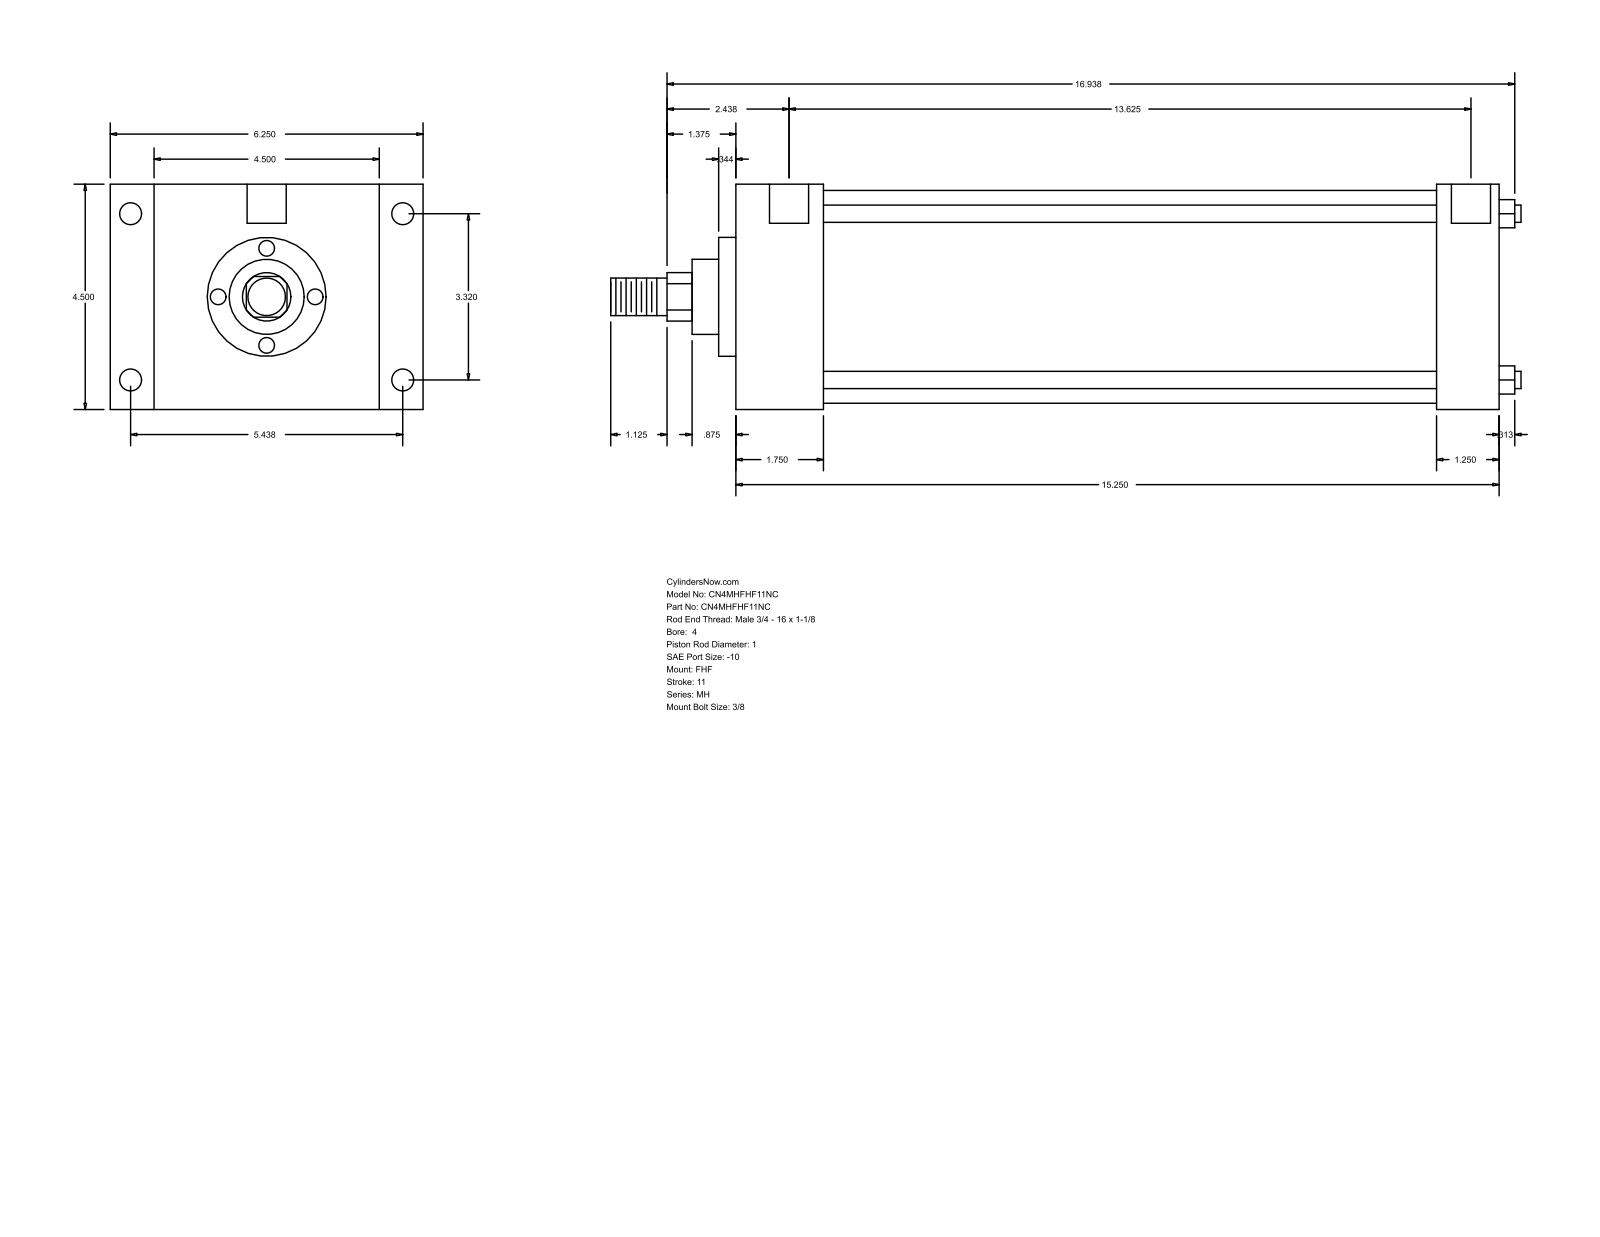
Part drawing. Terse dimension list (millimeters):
name: MH_FHF__0400_1
written by: GSSL Pune (CONFIG_CONTROL_DESIGN)
unit: mm
bodies: 0 solids, 90 faces (61 planar, 29 cylindrical, 0 other)
size: 461.96 × 158.75 × 114.3
holes: 4× ⌀8.73, 4× ⌀11.13, 2× ⌀19.84
bosses: 4× ⌀8.76, 1× ⌀107.95, 1× ⌀60.33, 1× ⌀38.1, 1× ⌀25.4, 1× ⌀19.05
rounds: 1× R12.29
face distances: 114.3, 387.35, 44.46, 342.89, 22.23, 136.53, 158.76, 355.6, 311.14, 31.75
hole spacings: 1.58, 84.32, 138.12, 161.82, 347.66, 349.24, 346.08
